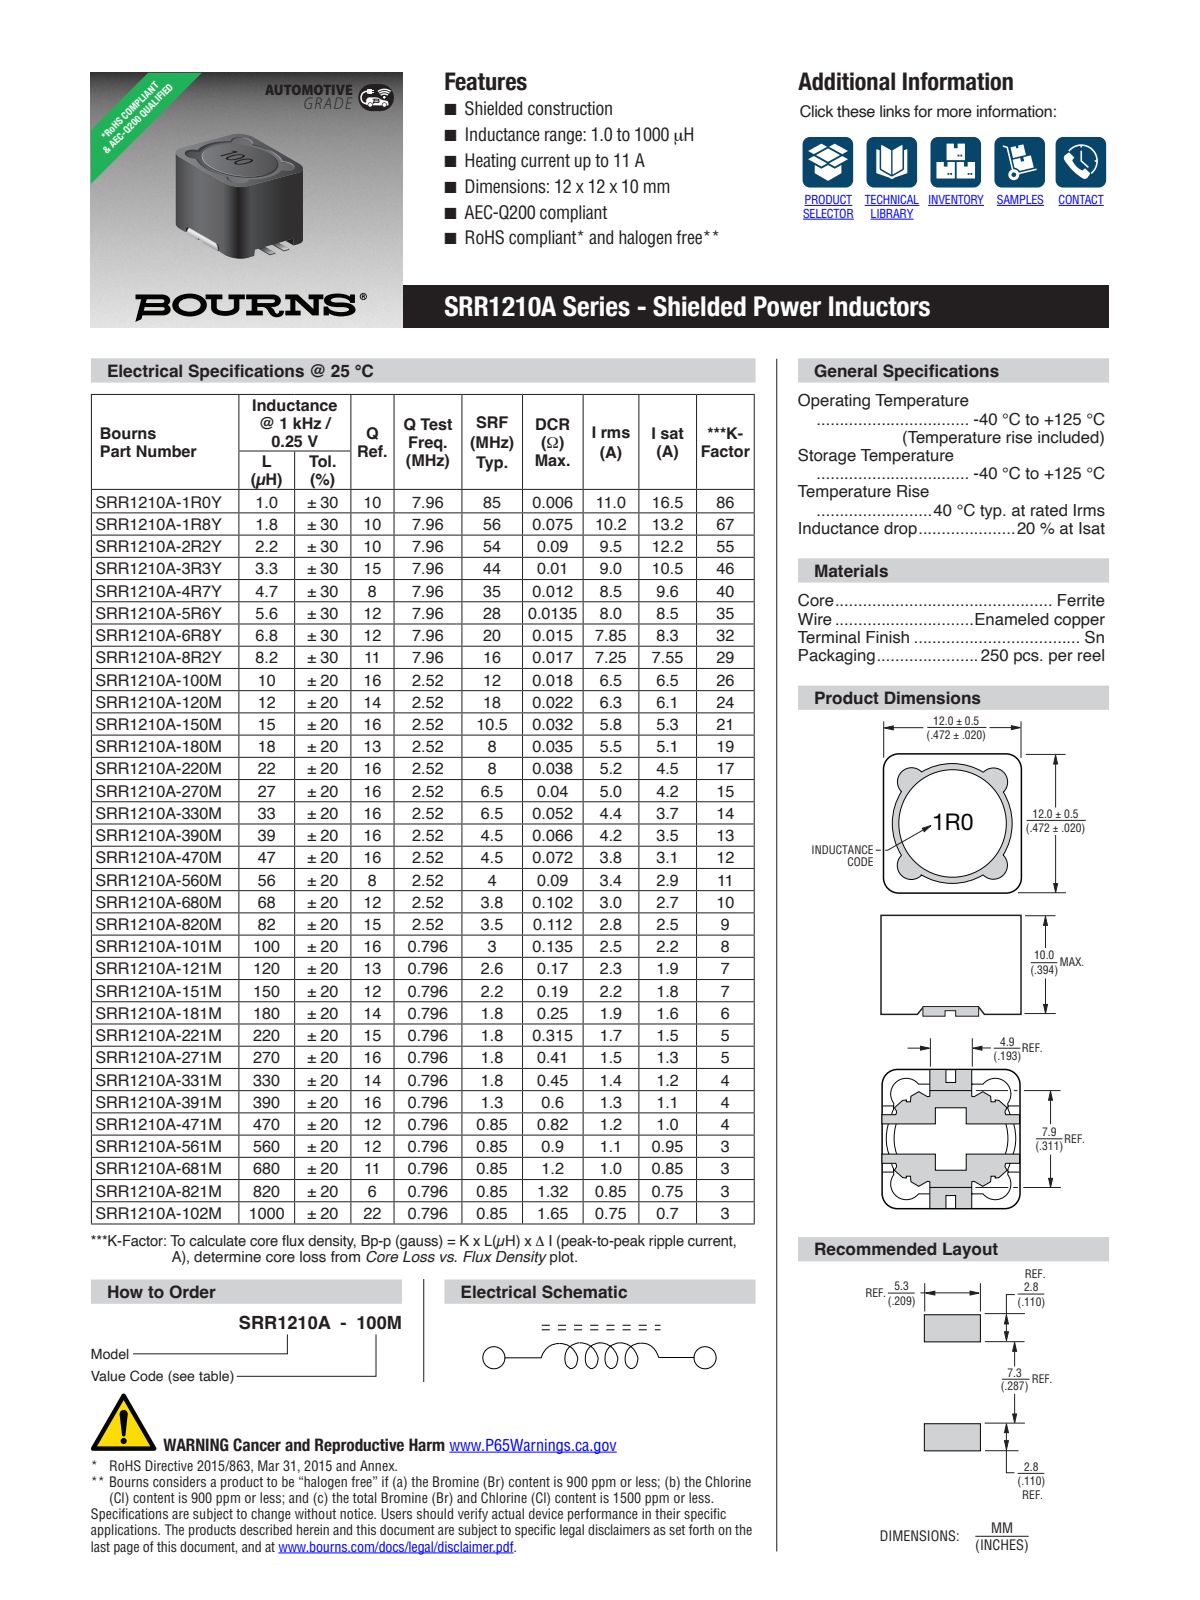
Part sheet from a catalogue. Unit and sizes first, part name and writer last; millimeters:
Units: millimetres
Overall size (bounding box): 12.4 × 12 × 9.25
Volume: 793 mm³ · Surface area: 1 476 mm²
Bodies: 8 solids, 195 faces (0 planar, 0 cylindrical, 195 other)
STEP written by: ZW3D to STEP translator (CONFIG_CONTROL_DESIGN)
